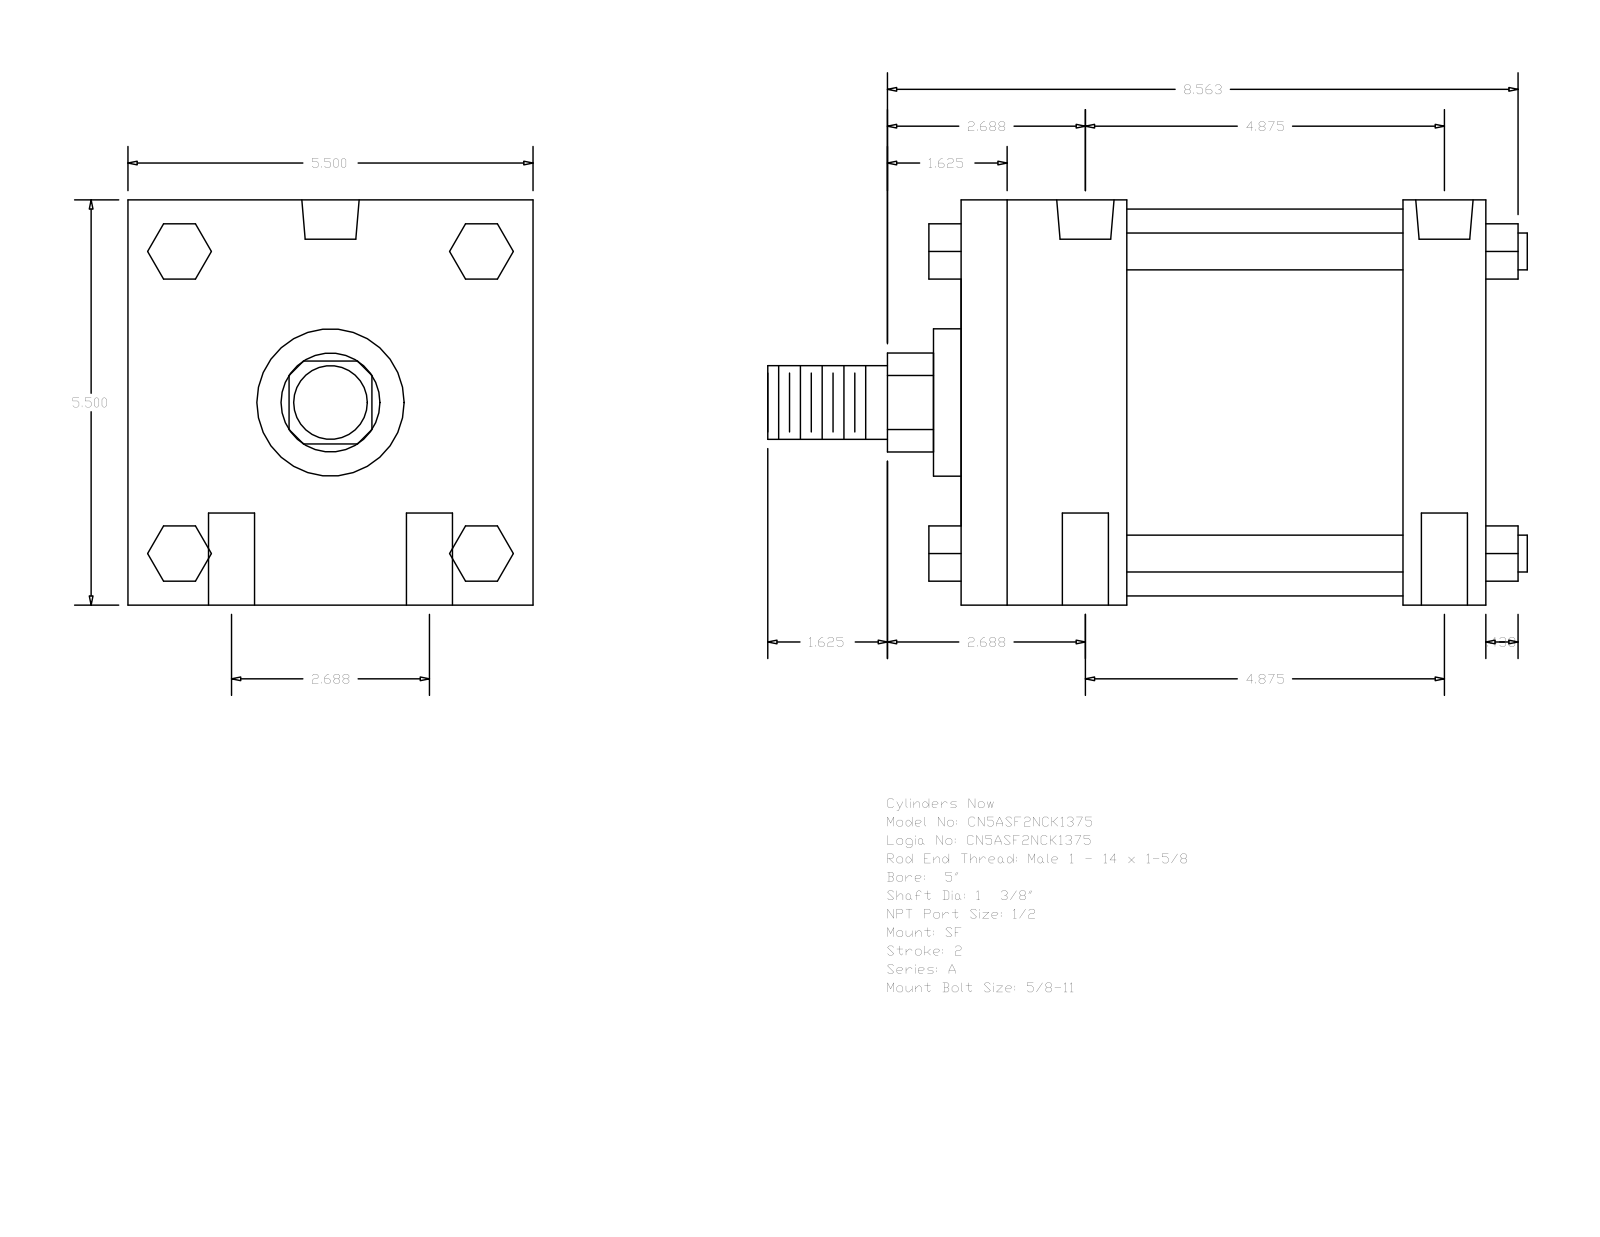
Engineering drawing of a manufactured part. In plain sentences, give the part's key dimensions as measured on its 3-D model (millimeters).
The part is named "A_SF__0500_1.375". Its 3-D file was written by "GSSL Pune (CONFIG_CONTROL_DESIGN)". It is 0 solids with 124 faces: 94 planar, 30 cylindrical and 0 other. Overall it measures 261.94 by 139.7 by 139.7 millimeters. Round holes: 4 of diameter 15.88, 2 of diameter 8.73, 2 of diameter 19.77. Round bosses or shafts: 4 of diameter 12.7, 1 of diameter 133.35, 1 of diameter 50.8, 1 of diameter 34.92, 1 of diameter 25.4. Partial cylindrical surfaces (rounded edges, fillets, slot ends): 1 of radius 17.06. The main face-to-face distances are 139.7, 180.98, 57.15, 28.58, 152.4, 95.25, 123.83, 19.05, 52.07, 90.18. The hole center spacings are 34.13, 128.45, 123.83, 68.26, 141.4, 119.05.
